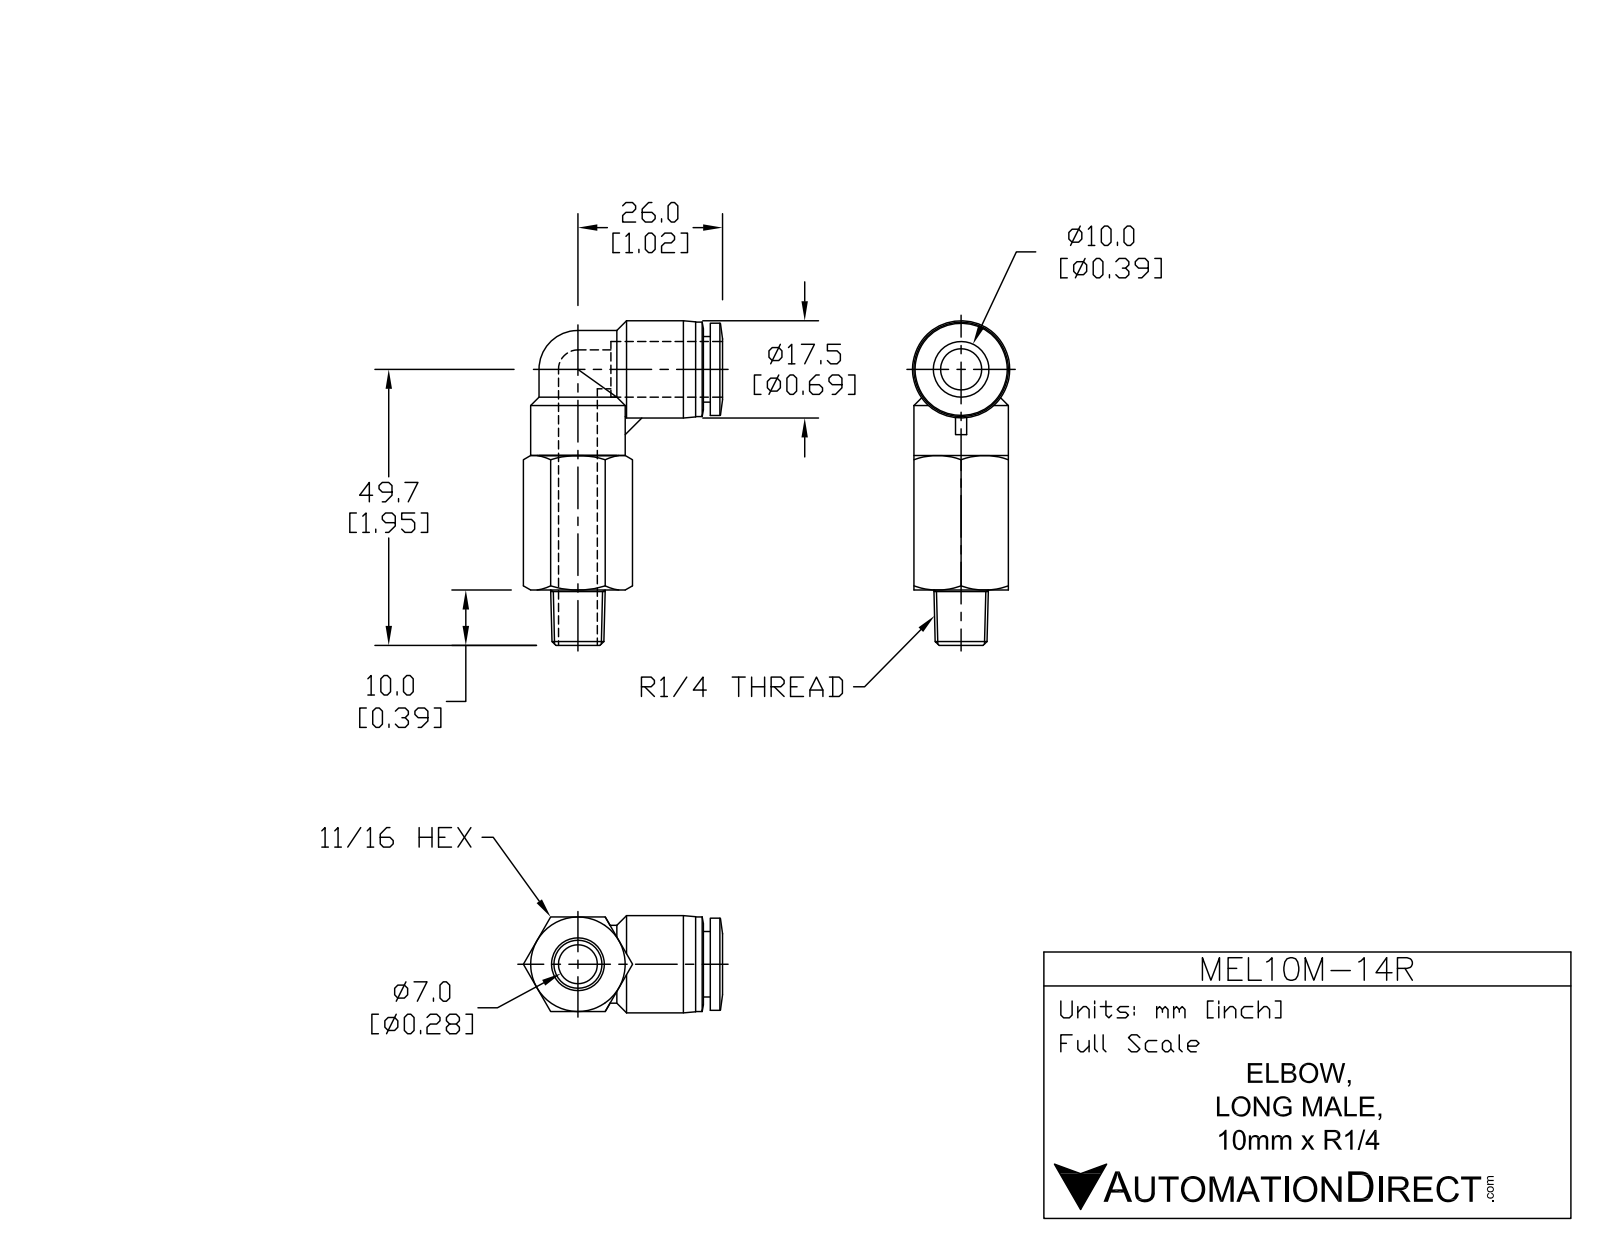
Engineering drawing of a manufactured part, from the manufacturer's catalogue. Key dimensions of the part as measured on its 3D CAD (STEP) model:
Part name (STEP PRODUCT): MEL10M-14R
STEP written by: SolidWorks 2015 (AUTOMOTIVE_DESIGN)
Units: inches
Bodies: 1 solid, 71 faces (16 planar, 20 cylindrical, 35 other)
Overall size (bounding box): 2.301 × 1.355 × 0.689
Volume: 0.704 in³ · Surface area: 9.633 in²
Round holes (diameter × count): ⌀0.276 ×2, ⌀0.406 ×1
Round bosses / shafts (diameter × count): ⌀0.669 ×2, ⌀0.689 ×1, ⌀0.654 ×1, ⌀0.551 ×1, ⌀0.465 ×1
Partial cylindrical surfaces — rounded edges, fillets, slot ends (radius × count): R0.276 ×1
Main face-to-face distances: 0.669, 0.049, 0.394, 0.659, 0.709, 0.295, 0.374, 0.079, 0.604, 0.055
